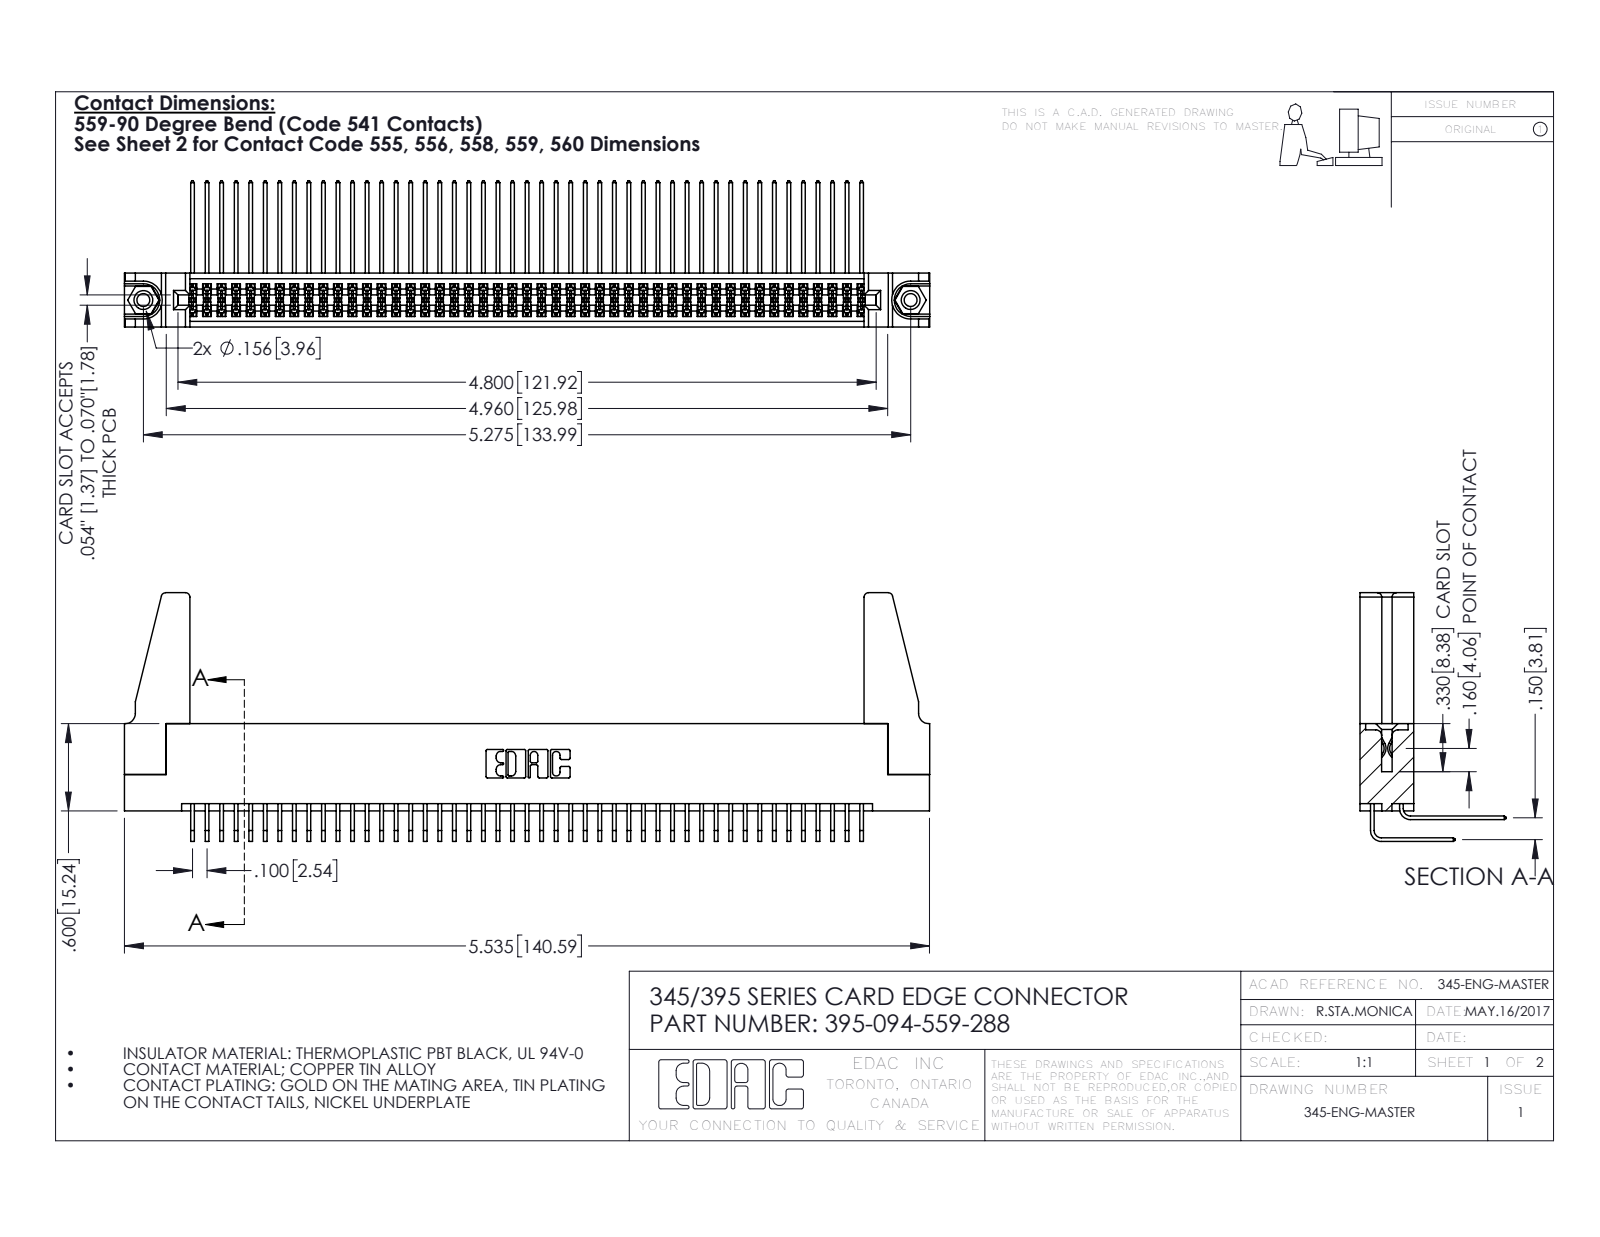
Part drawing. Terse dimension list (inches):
name: 345-292-001_559 Tail - 2; 345 Part_Flush Mounting Lugs - 0.156 Dia-TH; 395-094-559-288; 345-250-001_345-250-001-102 (+2 more)
written by: SolidWorks 2016 (CONFIG_CONTROL_DESIGN)
unit: in
bodies: 99 solids, 5138 faces (3442 planar, 1680 cylindrical, 16 other)
size: 5.536 × 1.709 × 1.005
volume: 1.068 in³; area: 41.59 in²
holes: 2× ⌀0.089, 2× ⌀0.125, 2× ⌀0.156, 1× ⌀0.064
bosses: 2× ⌀0.155
rounds: 141× R0.006, 22× R0.01, 8× R0.03, 6× R0.007, 6× R0.031, 3× R0.026, 2× R0.014, 2× R0.019
face distances: 0.072, 0.298, 0.37, 0.2, 0.098, 0.272, 0.025, 0.225, 0.175, 0.15
hole spacings: 0.27, 5.039, 5.275
